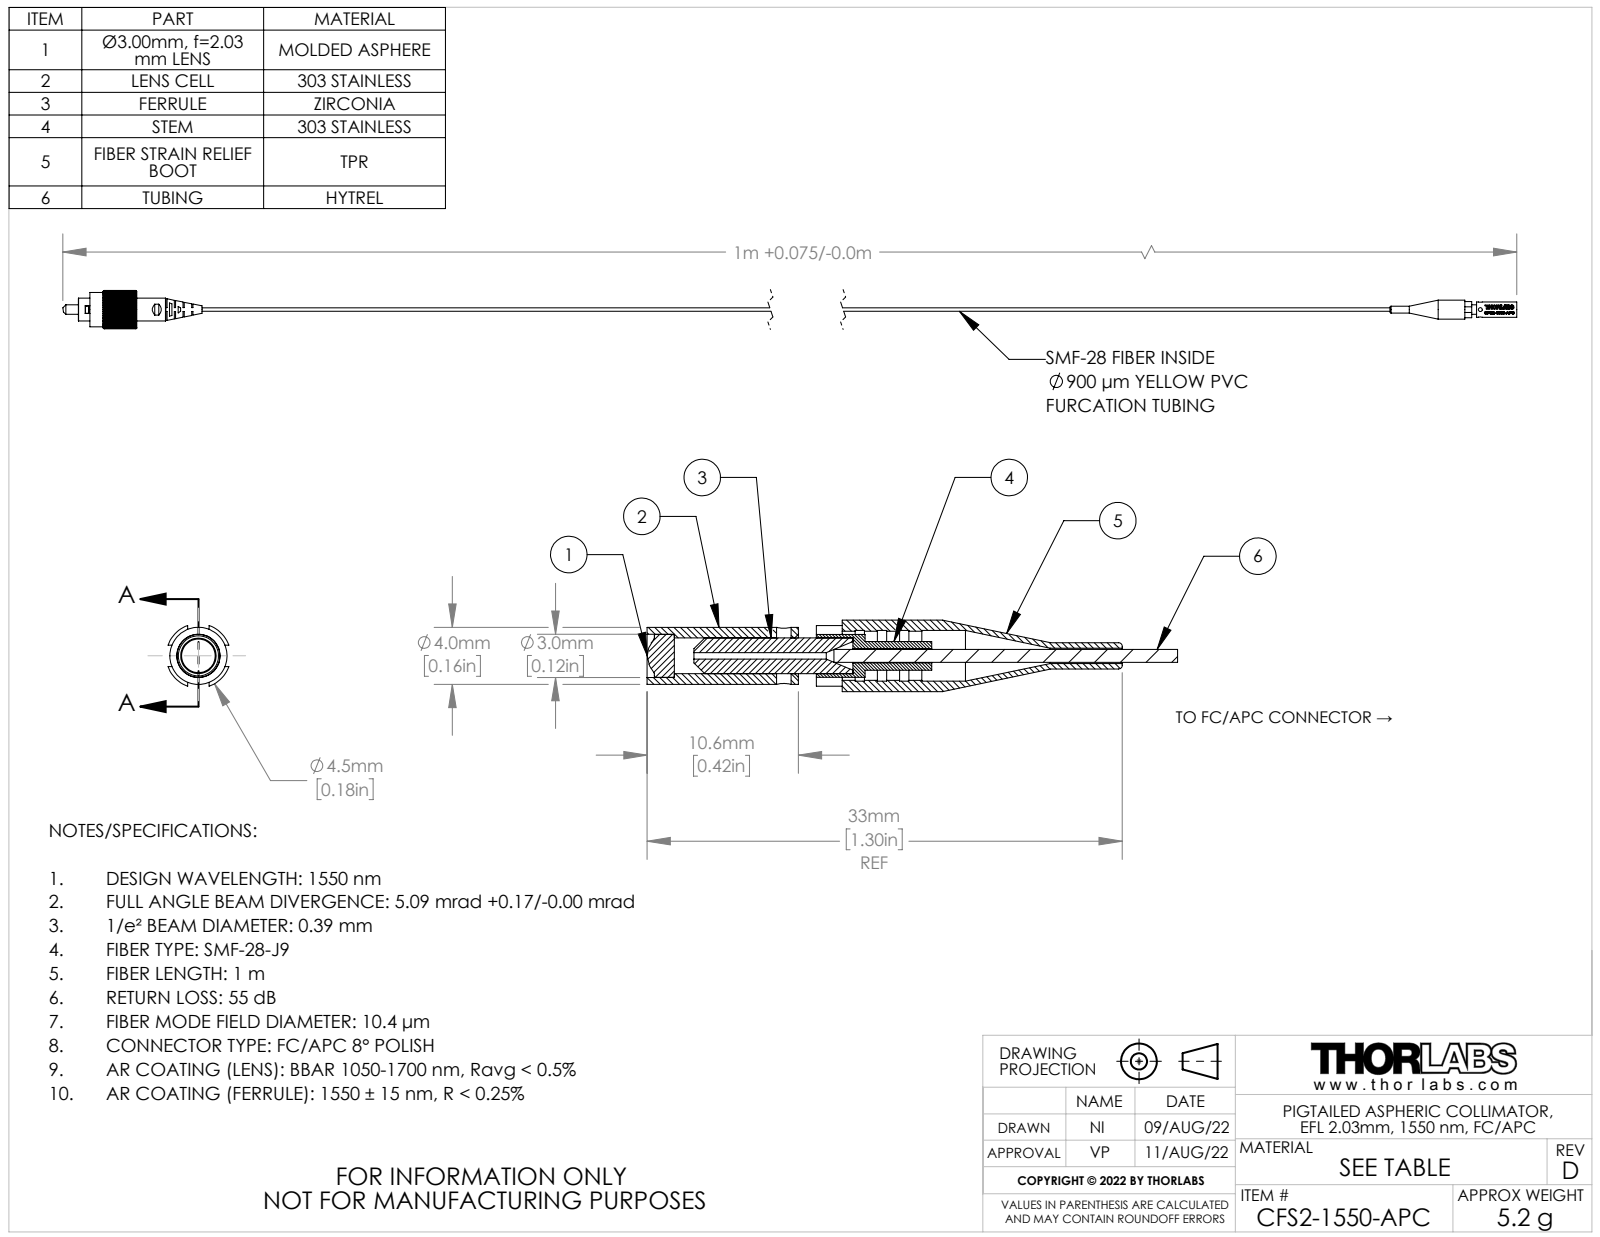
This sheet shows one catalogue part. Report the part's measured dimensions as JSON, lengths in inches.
{"part_name": "17377-E0W", "step_written_by": "SolidWorks 2018 (CONFIG_CONTROL_DESIGN)", "units": "inches", "bodies": {"solids": 9, "faces": 487, "planar": 241, "cylindrical": 198, "other": 48}, "overall_size": [40.331, 0.393, 0.393], "volume_in3": 0.103, "surface_area_in2": 9.181, "round_holes": [[0.04, 2], [0.018, 1], [0.039, 1], [0.042, 1], [0.055, 1], [0.098, 1], [0.119, 1], [0.119, 1], [0.12, 1], [0.135, 1], [0.14, 1], [0.155, 1]], "round_bosses_or_shafts": [[0.28, 1], [0.235, 1], [0.235, 1], [0.197, 1], [0.195, 1], [0.157, 1], [0.15, 1], [0.14, 1]], "partial_cylinders_radius": [[0.089, 1], [0.117, 1], [0.197, 1]], "face_to_face_distances": [0.267, 0.062, 0.04, 0.102, 0.089, 0.012, 0.178, 0.077, 0.101, 39.232]}
